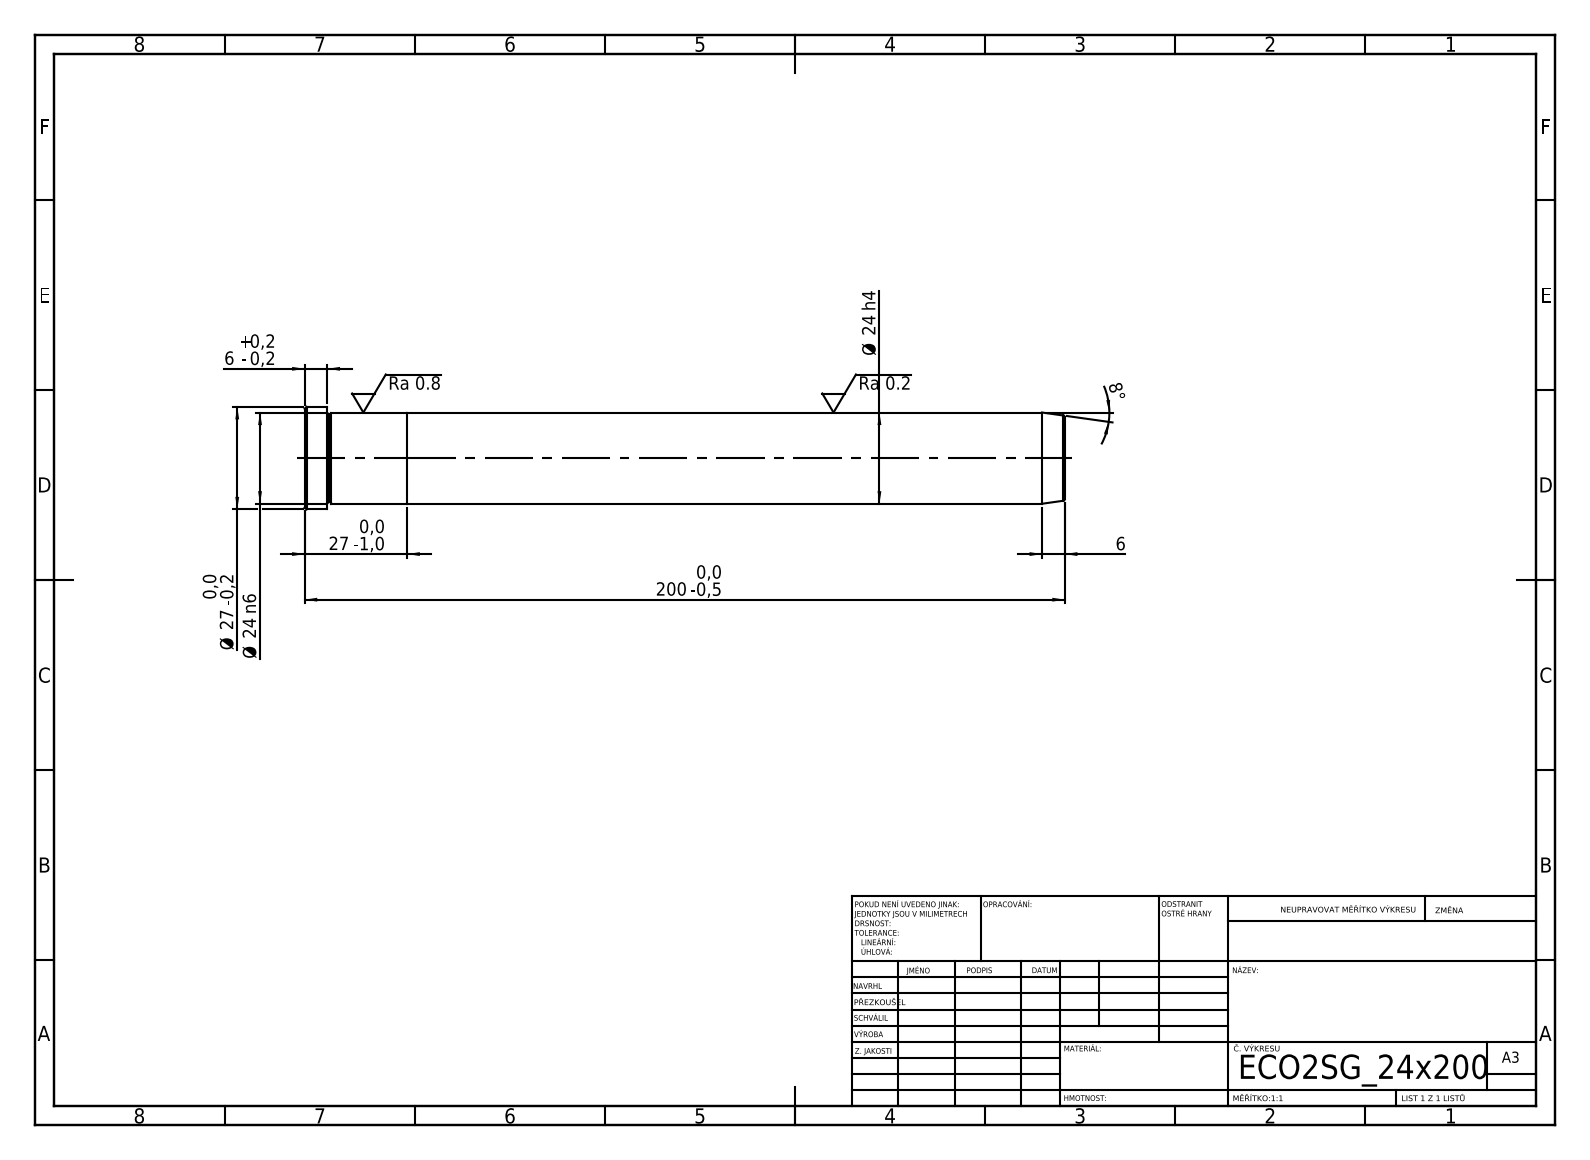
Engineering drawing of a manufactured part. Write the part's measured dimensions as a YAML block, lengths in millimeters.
step_written_by: "SolidWorks 2019 (CONFIG_CONTROL_DESIGN)"
units: millimeters
bodies: {solids: 2, faces: 21, planar: 5, cylindrical: 6, other: 10}
overall_size: [200, 27, 27]
volume: 90970
surface_area: 17117
round_bosses_or_shafts:
  - {diameter: 27, count: 1}
  - {diameter: 24, count: 1}
face_to_face_distances: [27, 173, 200, 194, 21, 6]
